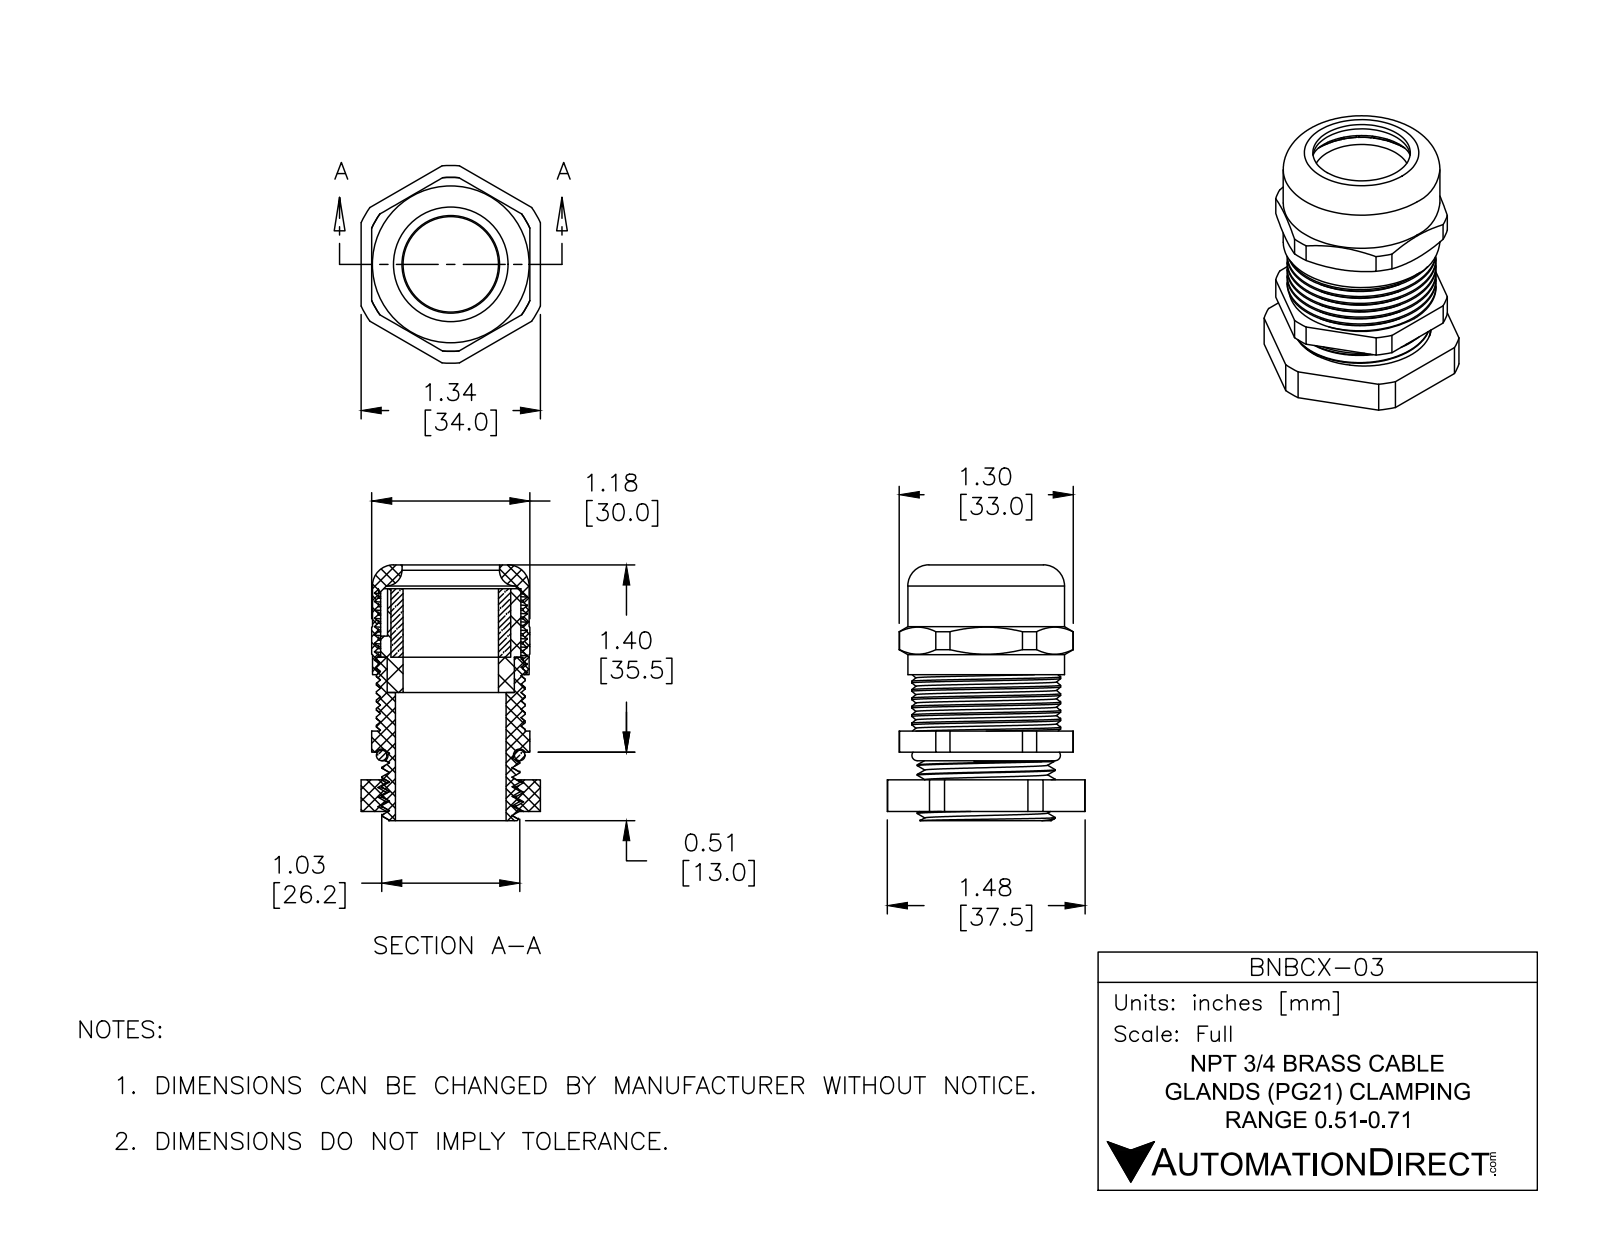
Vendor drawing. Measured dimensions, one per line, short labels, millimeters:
name: BNBCX-03
written by: SolidWorks 2015 (CONFIG_CONTROL_DESIGN)
unit: mm
bodies: 6 solids, 270 faces (135 planar, 102 cylindrical, 33 other)
size: 48.46 × 37.5 × 34
volume: 17 169 mm³; area: 21 233 mm²
holes: 1× ⌀18.1, 1× ⌀18.48, 1× ⌀20.98, 1× ⌀22.7, 1× ⌀24.1, 1× ⌀24.71, 1× ⌀27.44
bosses: 1× ⌀29.7, 1× ⌀28.2, 1× ⌀26.6, 1× ⌀26.16
rounds: 1× R16.5, 1× R16.5, 1× R18.75
face distances: 2, 32, 23.23, 6, 29.23, 0.5, 30, 22.53, 16.53, 6.7
